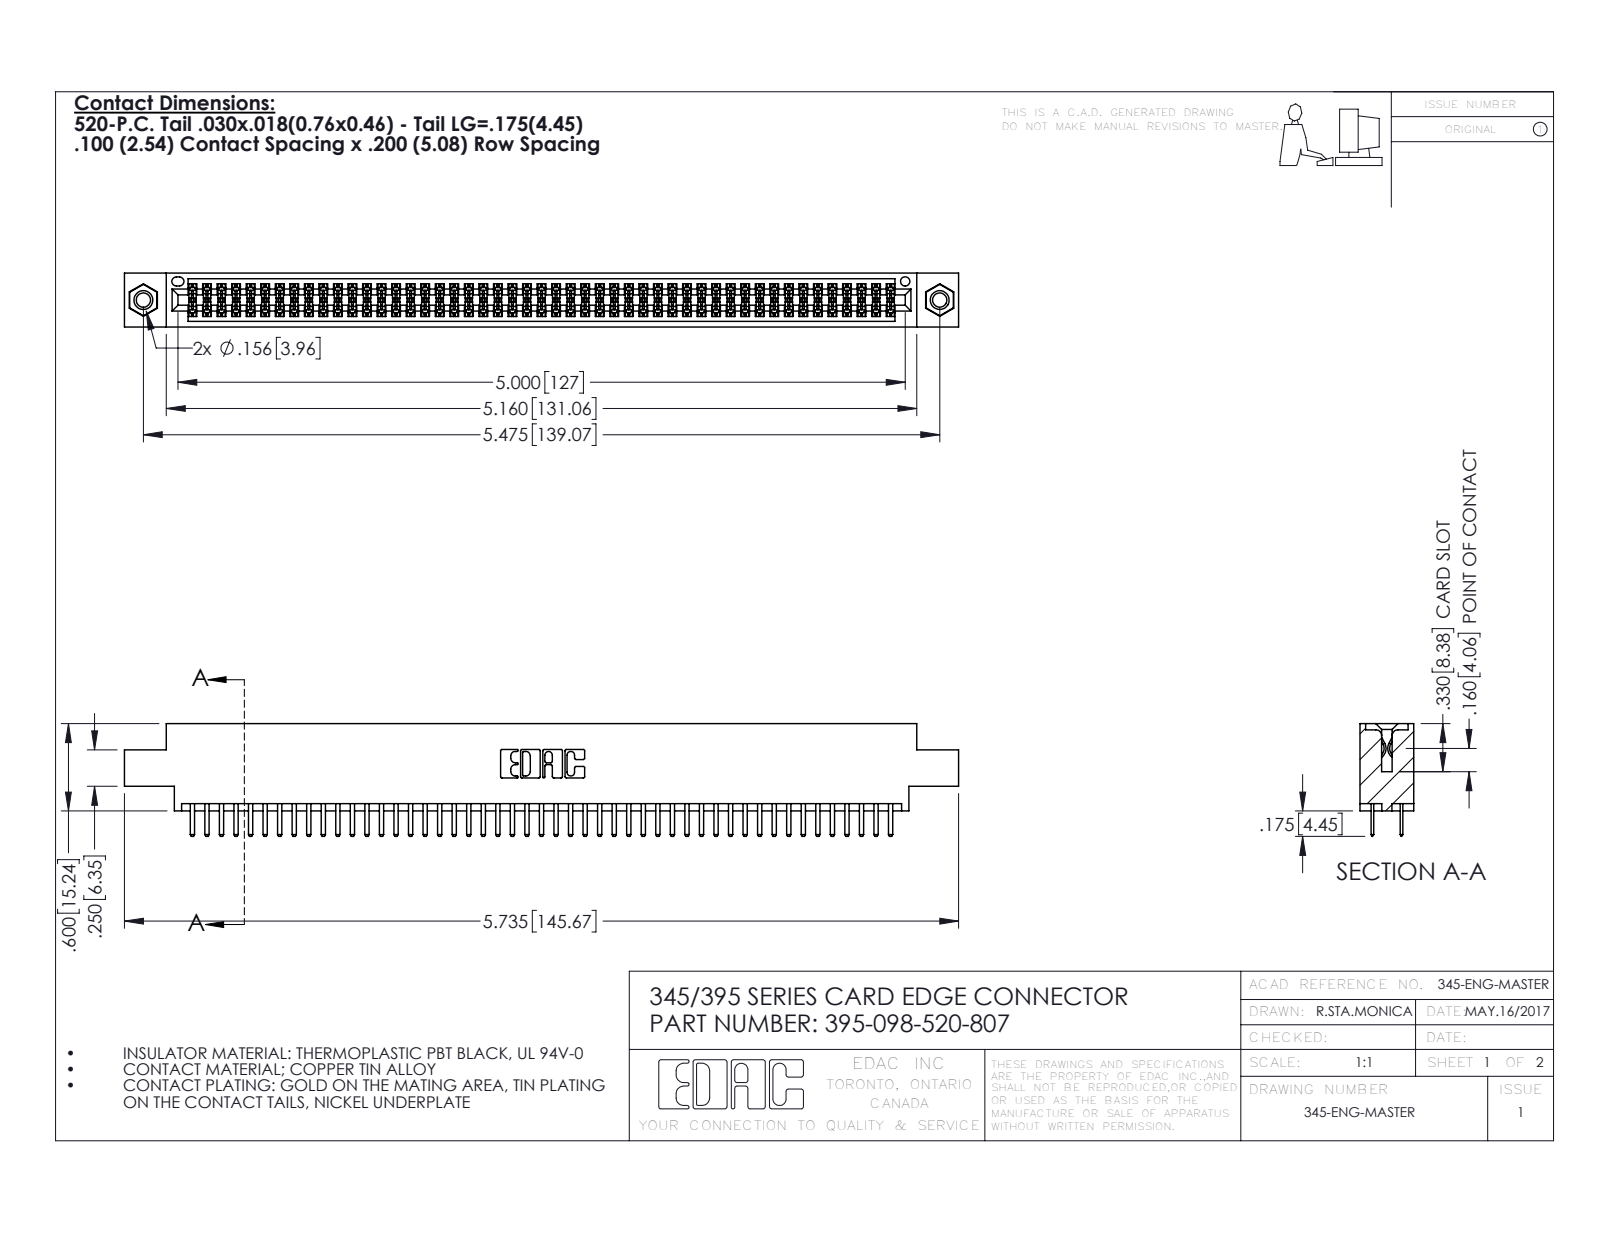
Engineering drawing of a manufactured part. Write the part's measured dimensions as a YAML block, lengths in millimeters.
part_name: "345-250-001_345-250-005-103; 345-292-001_345-293-120; 345 Part_0.170 Offset - 0.156 Dia-TI; 395-098-520-807"
step_written_by: "SolidWorks 2016 (CONFIG_CONTROL_DESIGN)"
units: millimeters
bodies: {solids: 101, faces: 5482, planar: 3546, cylindrical: 1920, other: 16}
overall_size: [145.7, 19.7, 9.4]
volume: 14000
surface_area: 20970
round_holes:
  - {diameter: 2.5, count: 2}
  - {diameter: 3.2, count: 2}
  - {diameter: 4, count: 2}
  - {diameter: 1.6, count: 1}
round_bosses_or_shafts:
  - {diameter: 3.9, count: 2}
partial_cylinders:
  - {radius: 0.2, count: 147}
  - {radius: 0.3, count: 102}
  - {radius: 0.3, count: 22}
  - {radius: 0.2, count: 6}
  - {radius: 0.8, count: 6}
  - {radius: 0.7, count: 3}
  - {radius: 0.4, count: 2}
  - {radius: 0.5, count: 2}
face_to_face_distances: [1.8, 7.6, 5.1, 9.4, 2.5, 6.9, 0.6, 5.7, 0.6, 1.8]
hole_center_spacings: [6.9, 133.1, 139.1]
